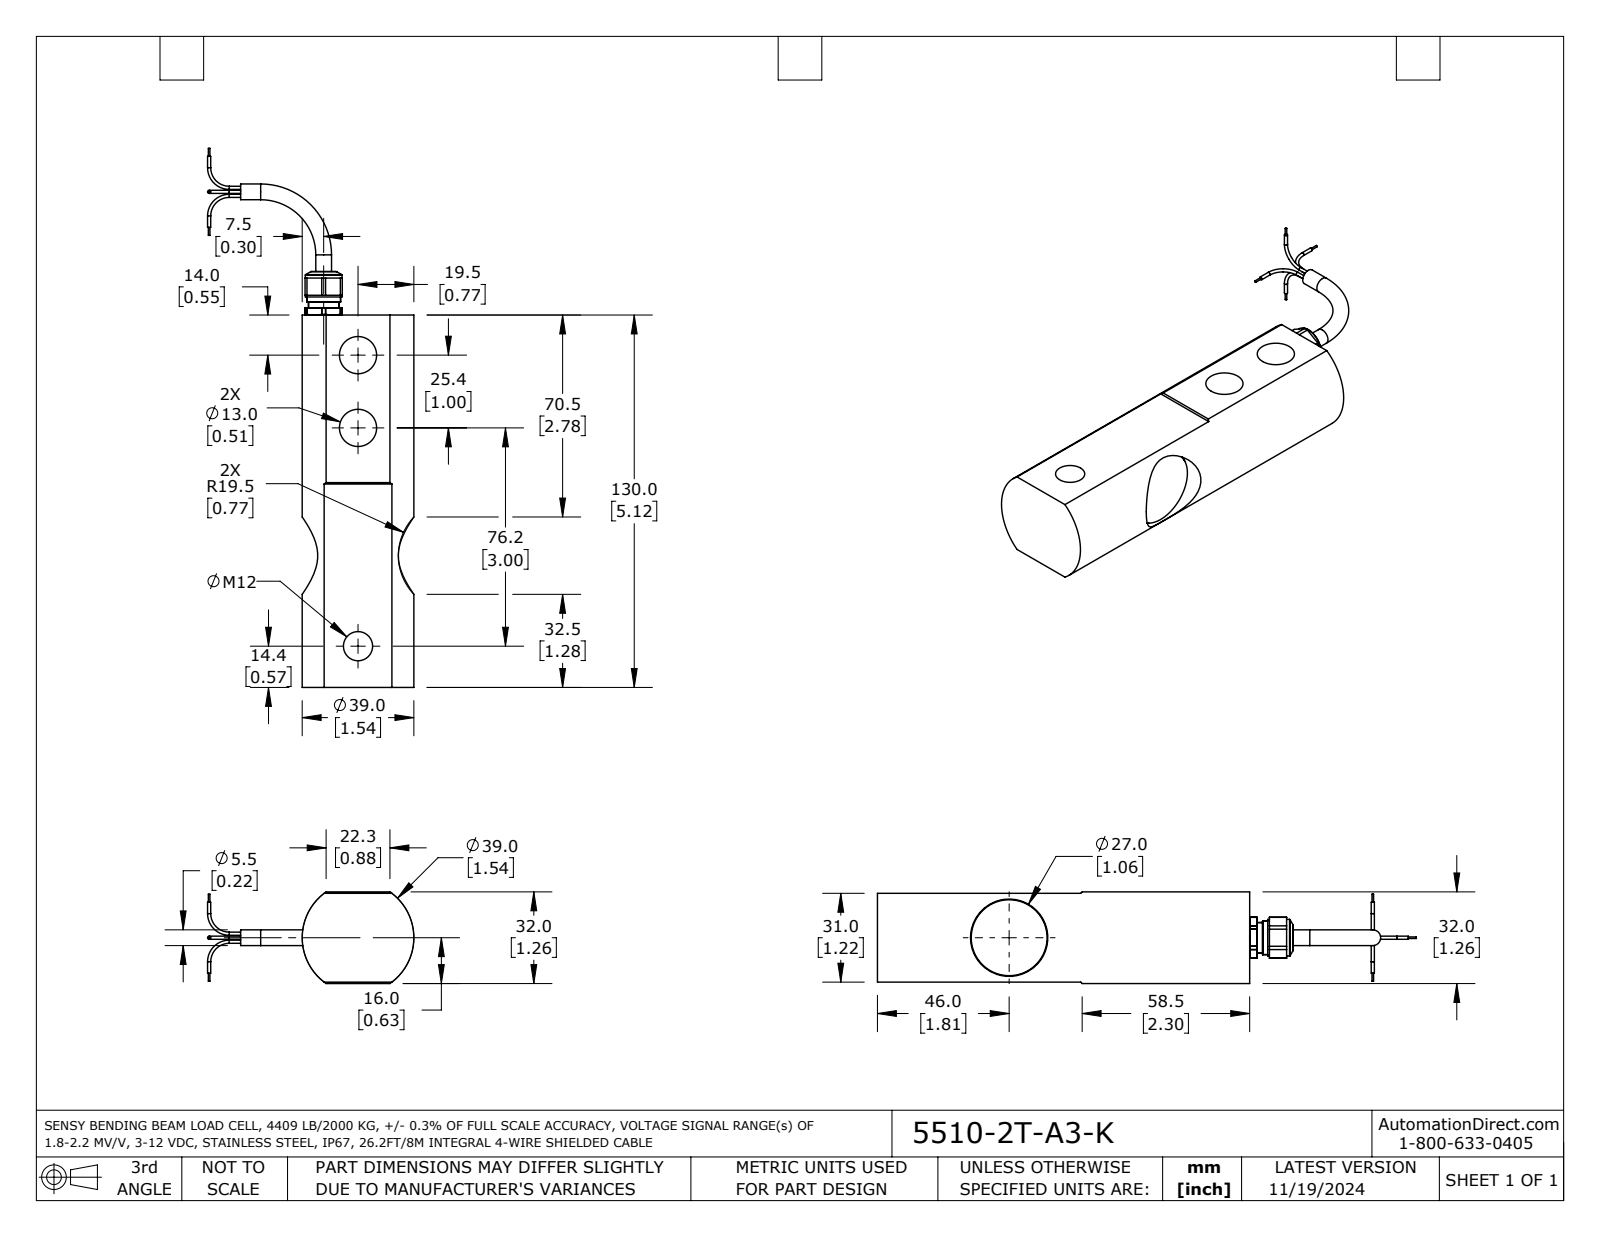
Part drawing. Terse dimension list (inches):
name: 5510-2T-A3-K
written by: SolidWorks 2021 (AUTOMOTIVE_DESIGN)
unit: in
bodies: 11 solids, 247 faces (67 planar, 112 cylindrical, 68 other)
size: 7.409 × 2.837 × 1.26
volume: 7.667 in³; area: 42.32 in²
holes: 2× ⌀0.512, 1× ⌀0.126, 1× ⌀0.157, 1× ⌀0.173, 1× ⌀0.24, 1× ⌀0.244, 1× ⌀0.329, 1× ⌀0.354, 1× ⌀0.402, 1× ⌀0.439, 1× ⌀1.063
bosses: 6× ⌀0.043, 2× ⌀0.217, 2× ⌀0.022, 1× ⌀1.043, 1× ⌀0.504, 1× ⌀0.464, 1× ⌀0.433, 1× ⌀0.417
rounds: 1× R0.281, 1× R0.768
face distances: 0.02, 1.24, 1.22, 5.118, 1.26, 1.029, 0.197, 0.512, 0.531, 5.65
hole spacings: 1, 3, 4
